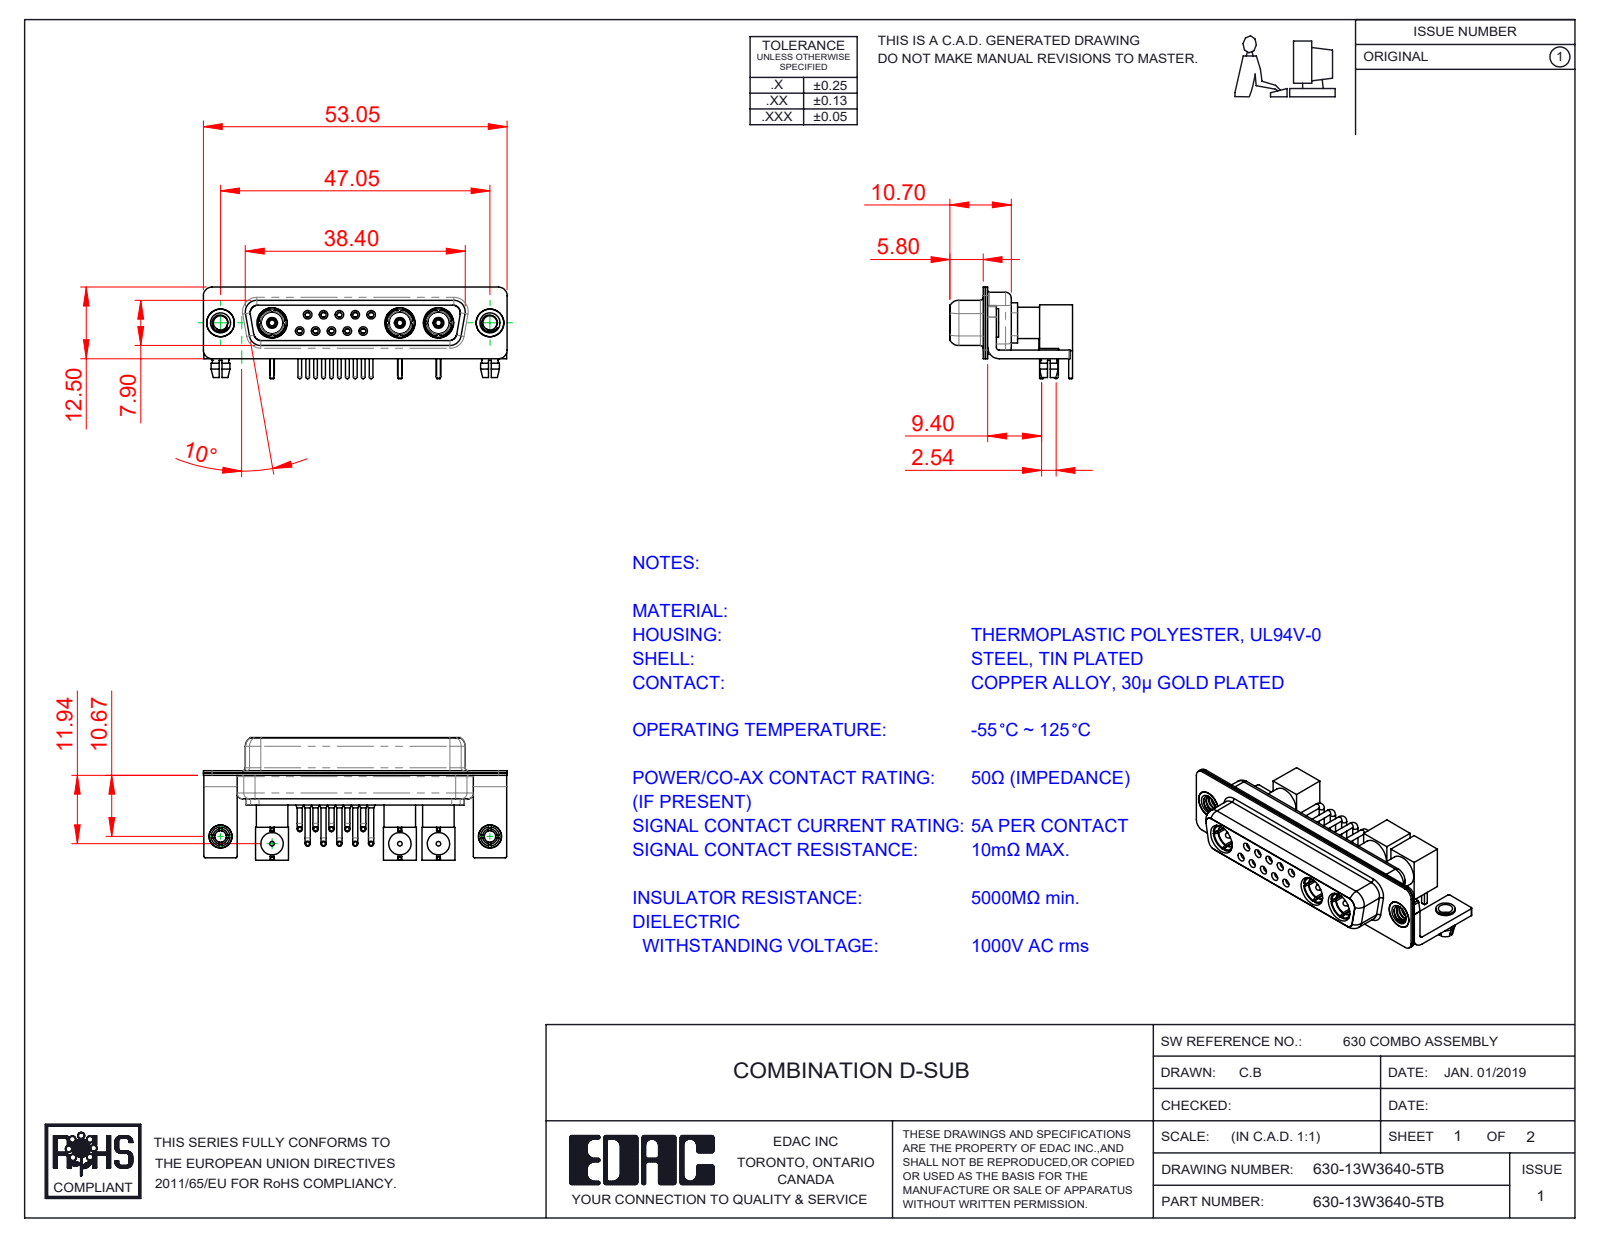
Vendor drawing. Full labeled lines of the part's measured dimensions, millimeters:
Part name (STEP PRODUCT): Insulator Pin_Straight PC Tail; 630Combo Shell Rear_25 Contacts; RA Back Shell; Co-Ax Plug Assy_RA (+8 more)
STEP written by: SolidWorks 2020 (CONFIG_CONTROL_DESIGN)
Units: millimetres
Bodies: 37 solids, 1443 faces (486 planar, 612 cylindrical, 345 other)
Overall size (bounding box): 53.05 × 21.41 × 16
Volume: 4 820 mm³ · Surface area: 11 682 mm²
Round holes (diameter × count): ⌀1.1 ×13, ⌀1.5 ×13, ⌀2 ×12, ⌀0.9 ×10, ⌀1.6 ×5, ⌀1.7 ×5, ⌀4.85 ×5, ⌀2.5 ×4, ⌀0.8 ×3, ⌀2.83 ×3, ⌀3.1 ×3, ⌀3.3 ×3
Round bosses / shafts (diameter × count): ⌀0.9 ×10, ⌀0.65 ×10, ⌀5 ×5, ⌀4 ×5, ⌀2.9 ×5, ⌀1.6 ×5, ⌀5.5 ×3, ⌀5.2 ×3
Partial cylindrical surfaces — rounded edges, fillets, slot ends (radius × count): R0.25 ×16, R1.5 ×16, R2 ×13, R1.35 ×8, R1.6 ×8, R0.5 ×5, R0.6 ×4, R0.65 ×4
Main face-to-face distances: 0.4, 1.4, 1.8, 0.45, 8.45, 0.8, 8.9, 1.35, 6.2, 7.05
Hole centre spacings: 3.16, 2.77, 5.54, 5.03, 5.04, 8.31, 7.48, 6.74
